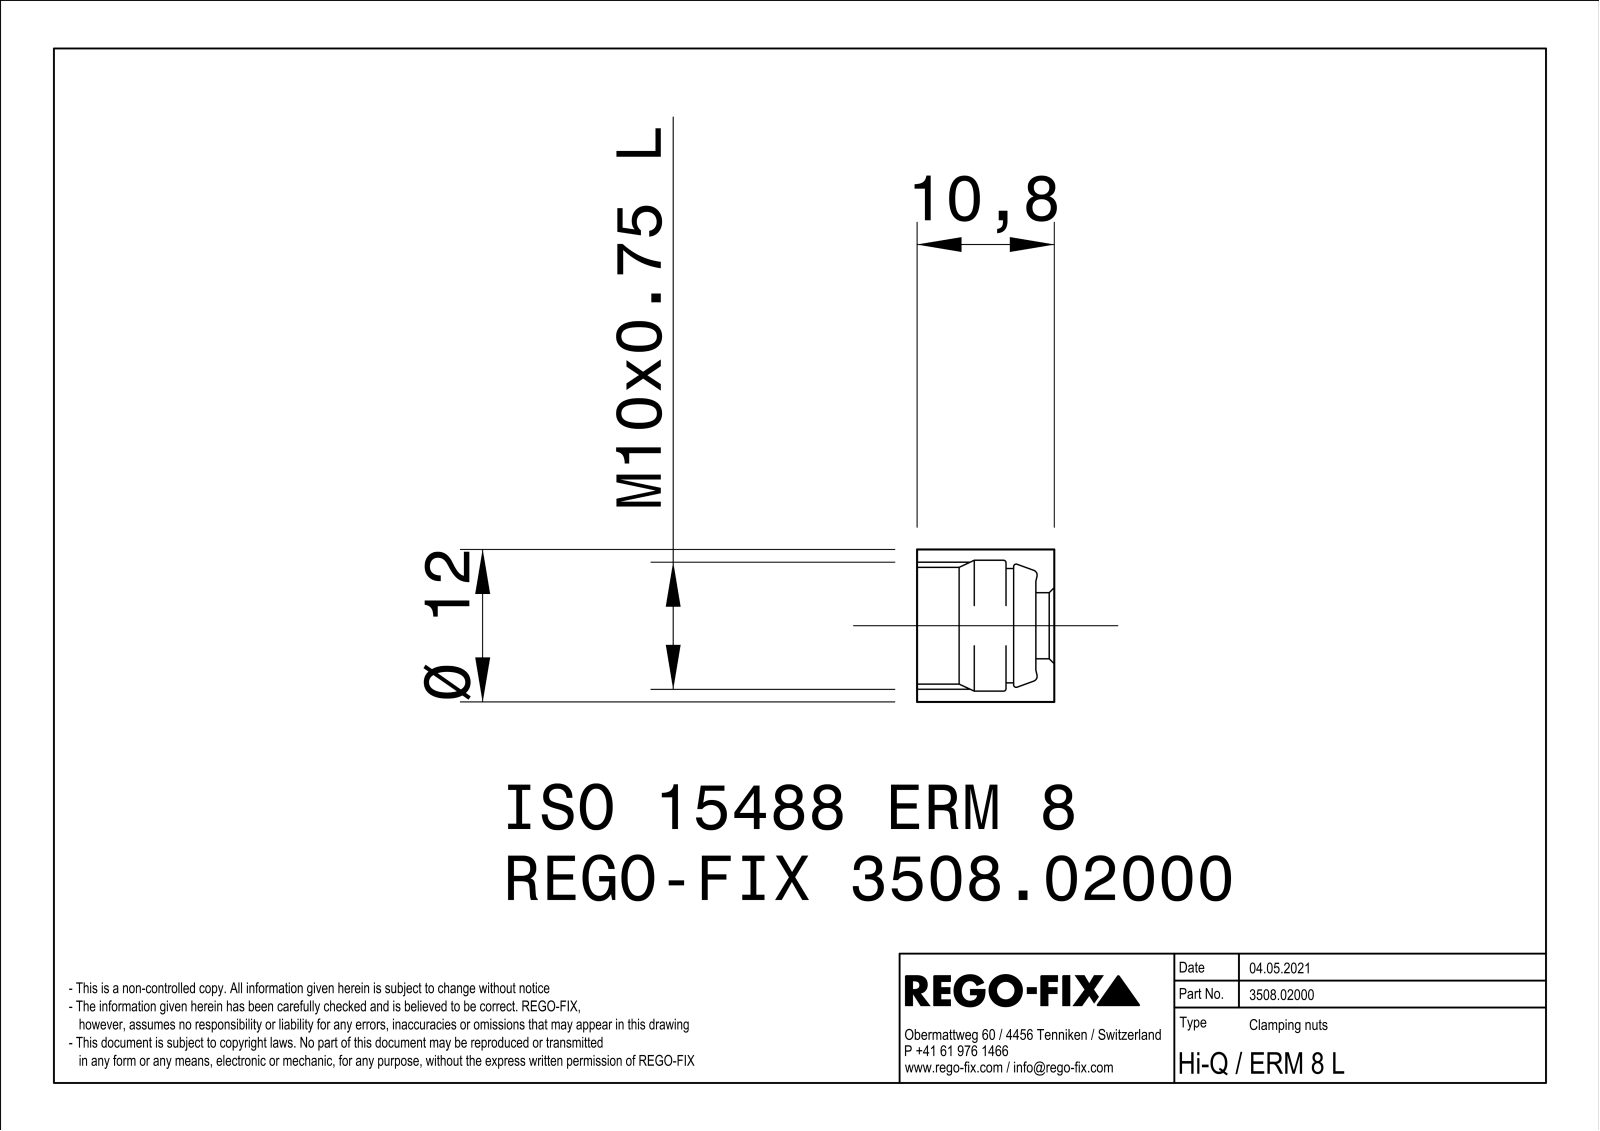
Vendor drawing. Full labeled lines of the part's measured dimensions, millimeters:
Part name (STEP PRODUCT): NOCUT
STEP written by: SIEMENS PLM Software Solid Edge ST10 (AUTOMOTIVE_DESIGN)
Units: millimetres
Bodies: 1 solid, 46 faces (23 planar, 6 cylindrical, 17 other)
Overall size (bounding box): 12 × 12 × 10.8
Volume: 469 mm³ · Surface area: 922 mm²
Round holes (diameter × count): ⌀5.2 ×1, ⌀9 ×1, ⌀9.19 ×1, ⌀10.3 ×1
Round bosses / shafts (diameter × count): ⌀12 ×1
Main face-to-face distances: 10.8, 1.45, 9.35, 2.5, 3.8, 2.35, 7, 3.2, 1.75, 0.6
